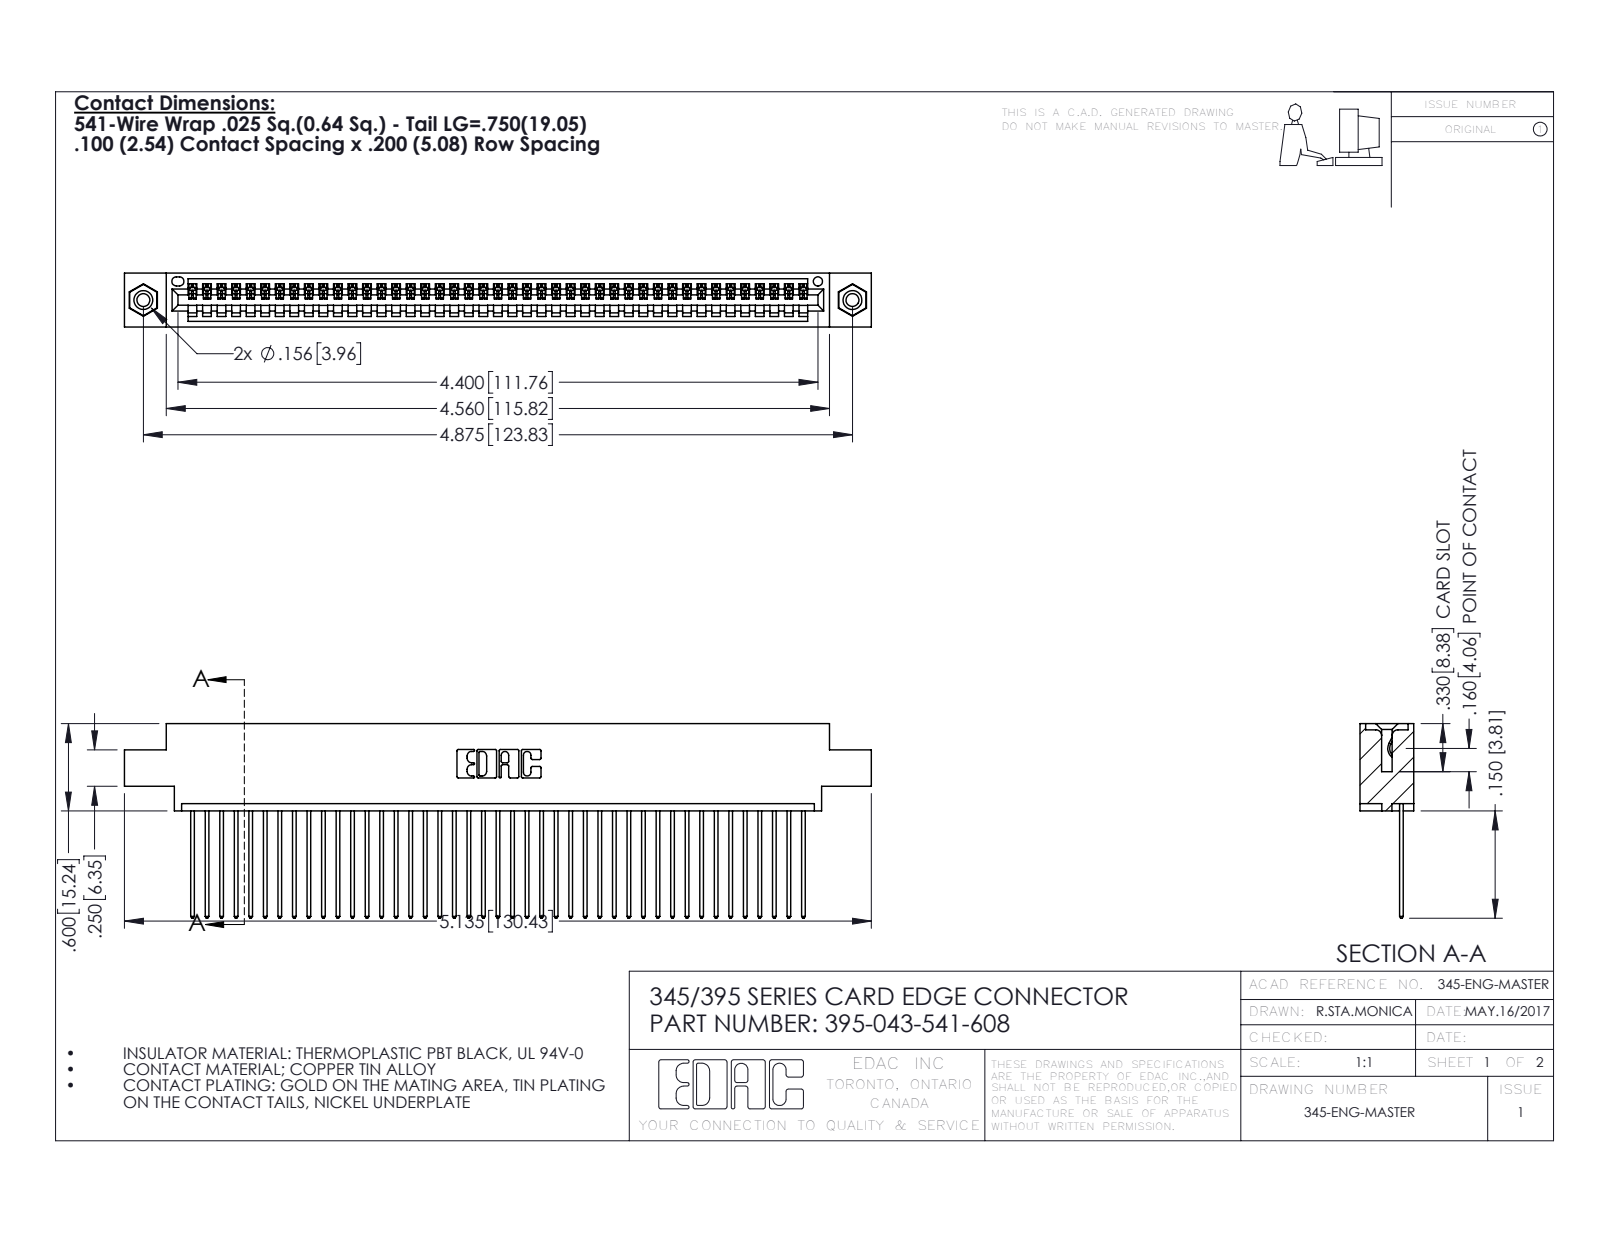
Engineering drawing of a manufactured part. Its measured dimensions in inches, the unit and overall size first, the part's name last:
Units: inches
Overall size (bounding box): 5.135 × 1.337 × 0.37
Round holes (diameter × count): ⌀0.089 ×2, ⌀0.125 ×2, ⌀0.156 ×2, ⌀0.064 ×1
Round bosses / shafts (diameter × count): ⌀0.155 ×2
Partial cylindrical surfaces — rounded edges, fillets, slot ends (radius × count): R0.006 ×86, R0.01 ×86, R0.01 ×22, R0.007 ×6, R0.031 ×6, R0.026 ×3, R0.031 ×2, R0.04 ×2
Main face-to-face distances: 0.072, 0.298, 0.37, 0.098, 0.272, 0.025, 0.2, 0.225, 0.175, 0.149
Hole centre spacings: 0.27, 4.639, 4.875
Volume: 0.758 in³ · Surface area: 27.12 in²
Bodies: 46 solids, 2684 faces (1836 planar, 832 cylindrical, 16 other)
Part name (STEP PRODUCT): 345-250-001_345-250-003-102; 345-292-001_345-293-141; 395-043-541-608; 345 Part_0.170 Offset - 0.156 Dia-TI
STEP written by: SolidWorks 2016 (CONFIG_CONTROL_DESIGN)
